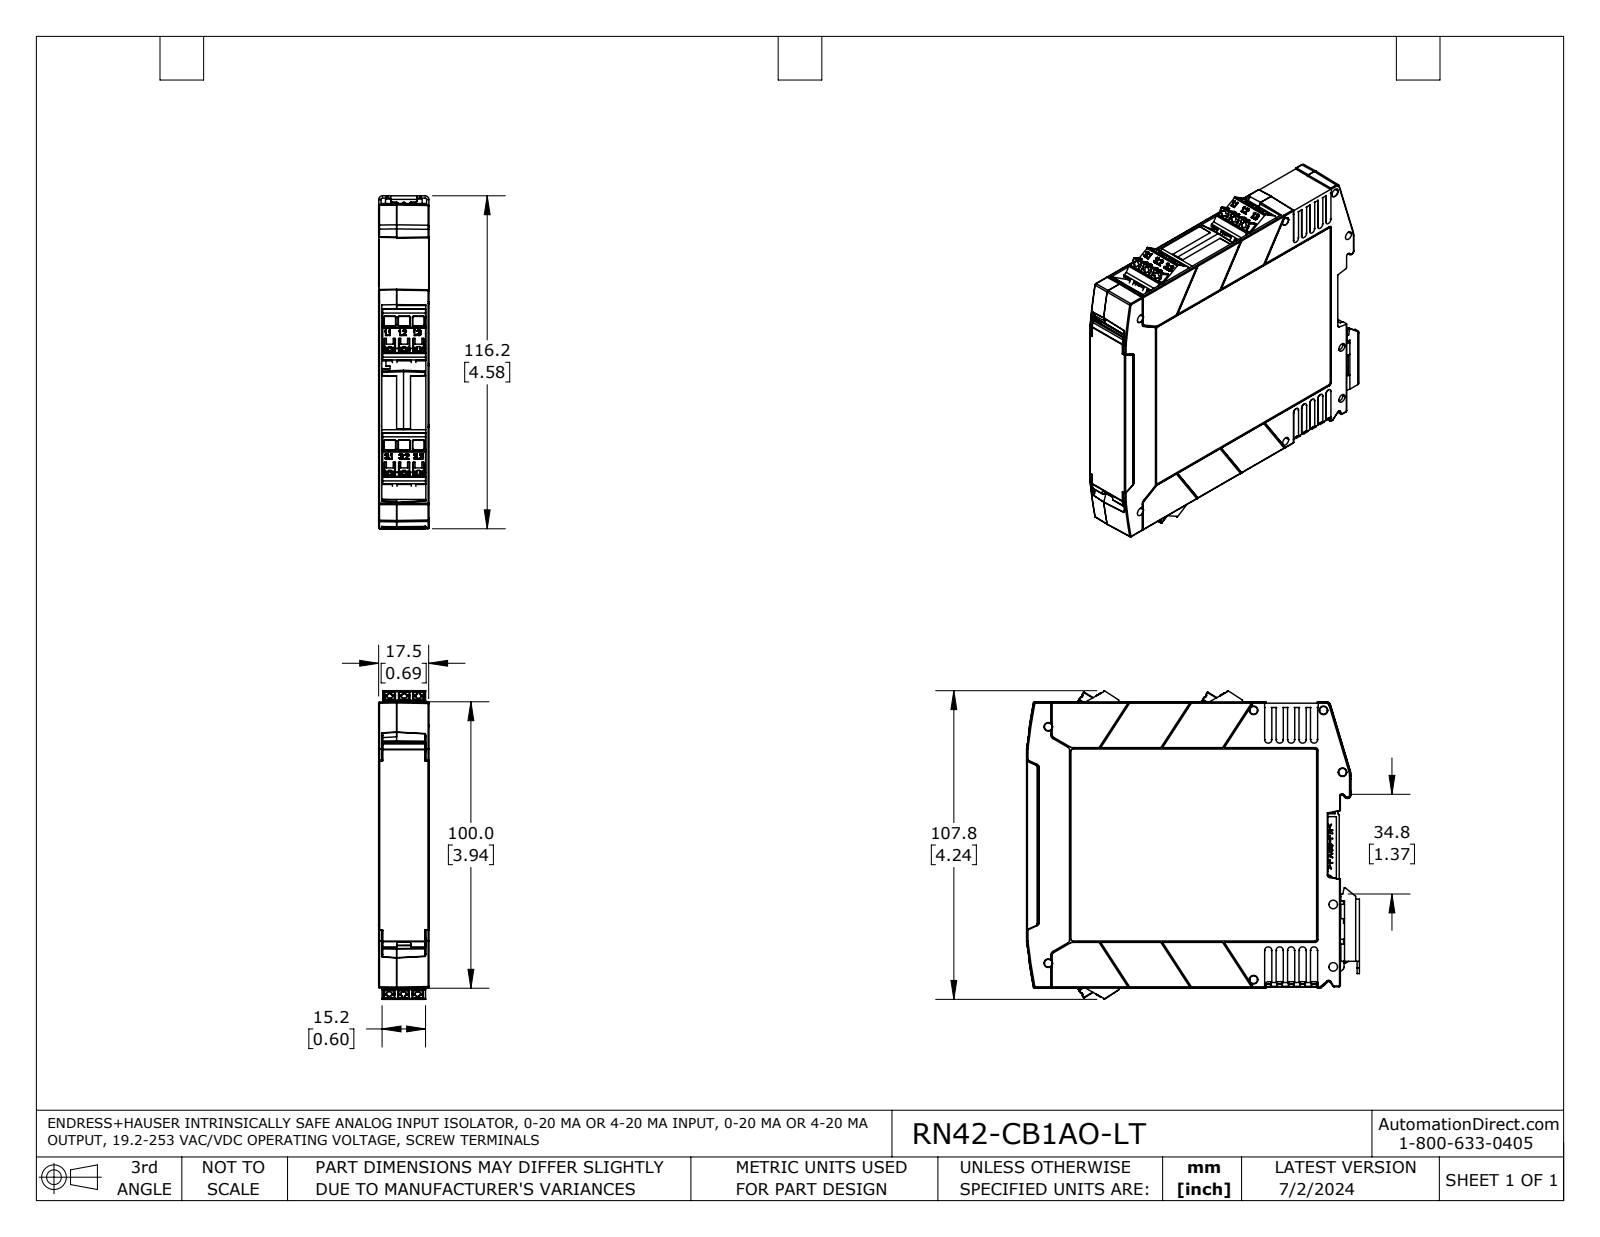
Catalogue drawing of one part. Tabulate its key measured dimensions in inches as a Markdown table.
| quantity | value |
| --- | --- |
| part name | RN42-CB1AO-LT |
| STEP written by | SolidWorks 2021 (AUTOMOTIVE_DESIGN) |
| units | inches |
| bodies | 6 solids, 4355 faces (2900 planar, 793 cylindrical, 662 other) |
| overall size | 4.577 × 4.242 × 0.693 |
| volume | 12.22 in³ |
| surface area | 112.1 in² |
| round holes (diameter × count) | 0.059 × 9, 0.11 × 9, 0.118 × 5, 0.135 × 2, 0.009 × 1, 0.14 × 1, 0.184 × 1 |
| round bosses / shafts (diameter × count) | 0.053 × 2 |
| partial cylindrical surfaces (radius × count) | 0.008 × 135, 0.02 × 109, 0.012 × 55, 0.004 × 26, 0.039 × 25, 0.047 × 9, 0.114 × 9, 0.005 × 8 |
| main face-to-face distances | 0.688, 0.692, 0.052, 0.048, 0.641, 0.043, 0.047, 0.031, 0.039, 0.649 |
| hole center spacings | 0.197, 0.394, 1.439, 1.44, 1.426, 1.426, 1.479, 1.48 |
